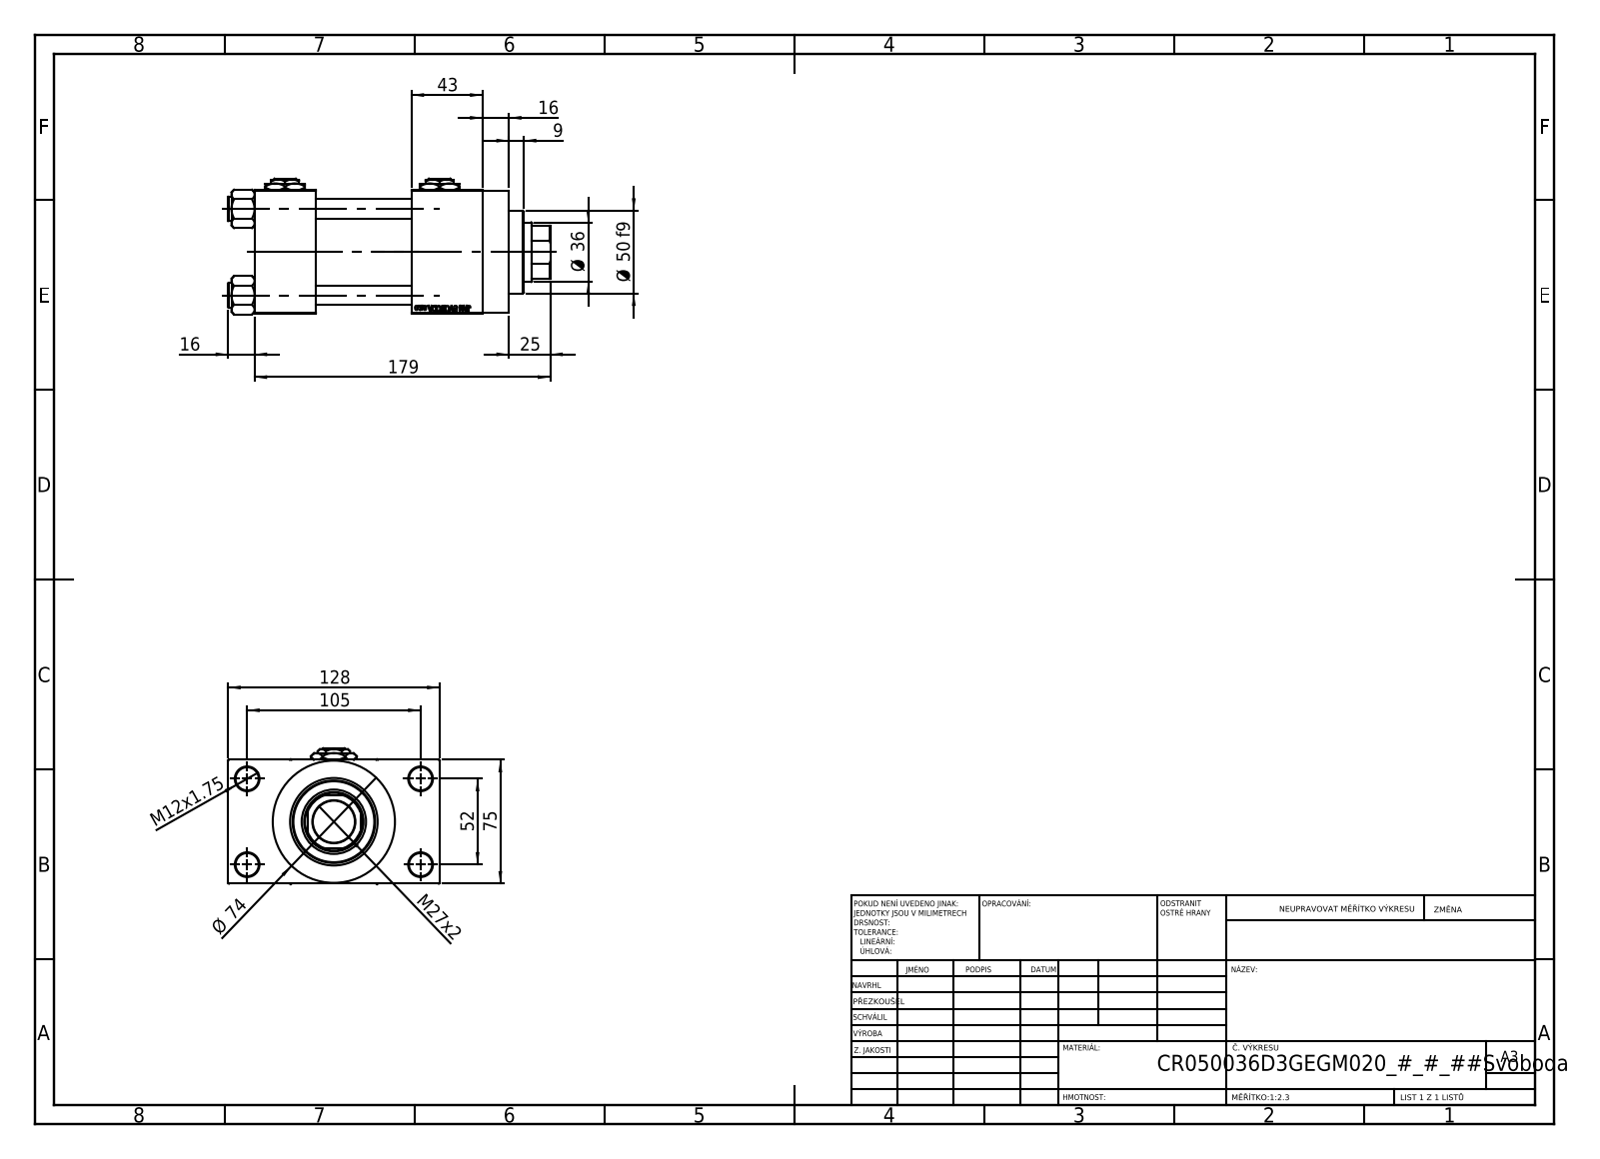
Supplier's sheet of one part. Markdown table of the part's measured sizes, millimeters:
| quantity | value |
| --- | --- |
| part name | V215CR_D_Body; V215_VC_A; V215CR_VCP_D; V215CR_D_TYCINKA (+2 more) |
| STEP written by | SolidWorks 2019 (CONFIG_CONTROL_DESIGN) |
| units | millimeters |
| bodies | 13 solids, 1205 faces (545 planar, 100 cylindrical, 560 other) |
| overall size | 195 × 128 × 82.27 |
| volume | 821 972 mm³ |
| surface area | 178 028 mm² |
| round holes (diameter × count) | 12 × 4, 14 × 4, 7 × 2, 20.96 × 2, 30 × 2, 25.5 × 1, 36 × 1, 39 × 1, 41 × 1, 53 × 1 |
| round bosses / shafts (diameter × count) | 15 × 4, 74 × 1, 56 × 1, 50 × 1 |
| partial cylindrical surfaces (radius × count) | 17.5 × 1 |
| main face-to-face distances | 75, 58, 37, 95, 101.5, 26.5, 138, 43, 101, 16 |
| hole center spacings | 26.35, 36.98, 52.3, 58.43, 58.59, 78.65, 94.37, 52 |
